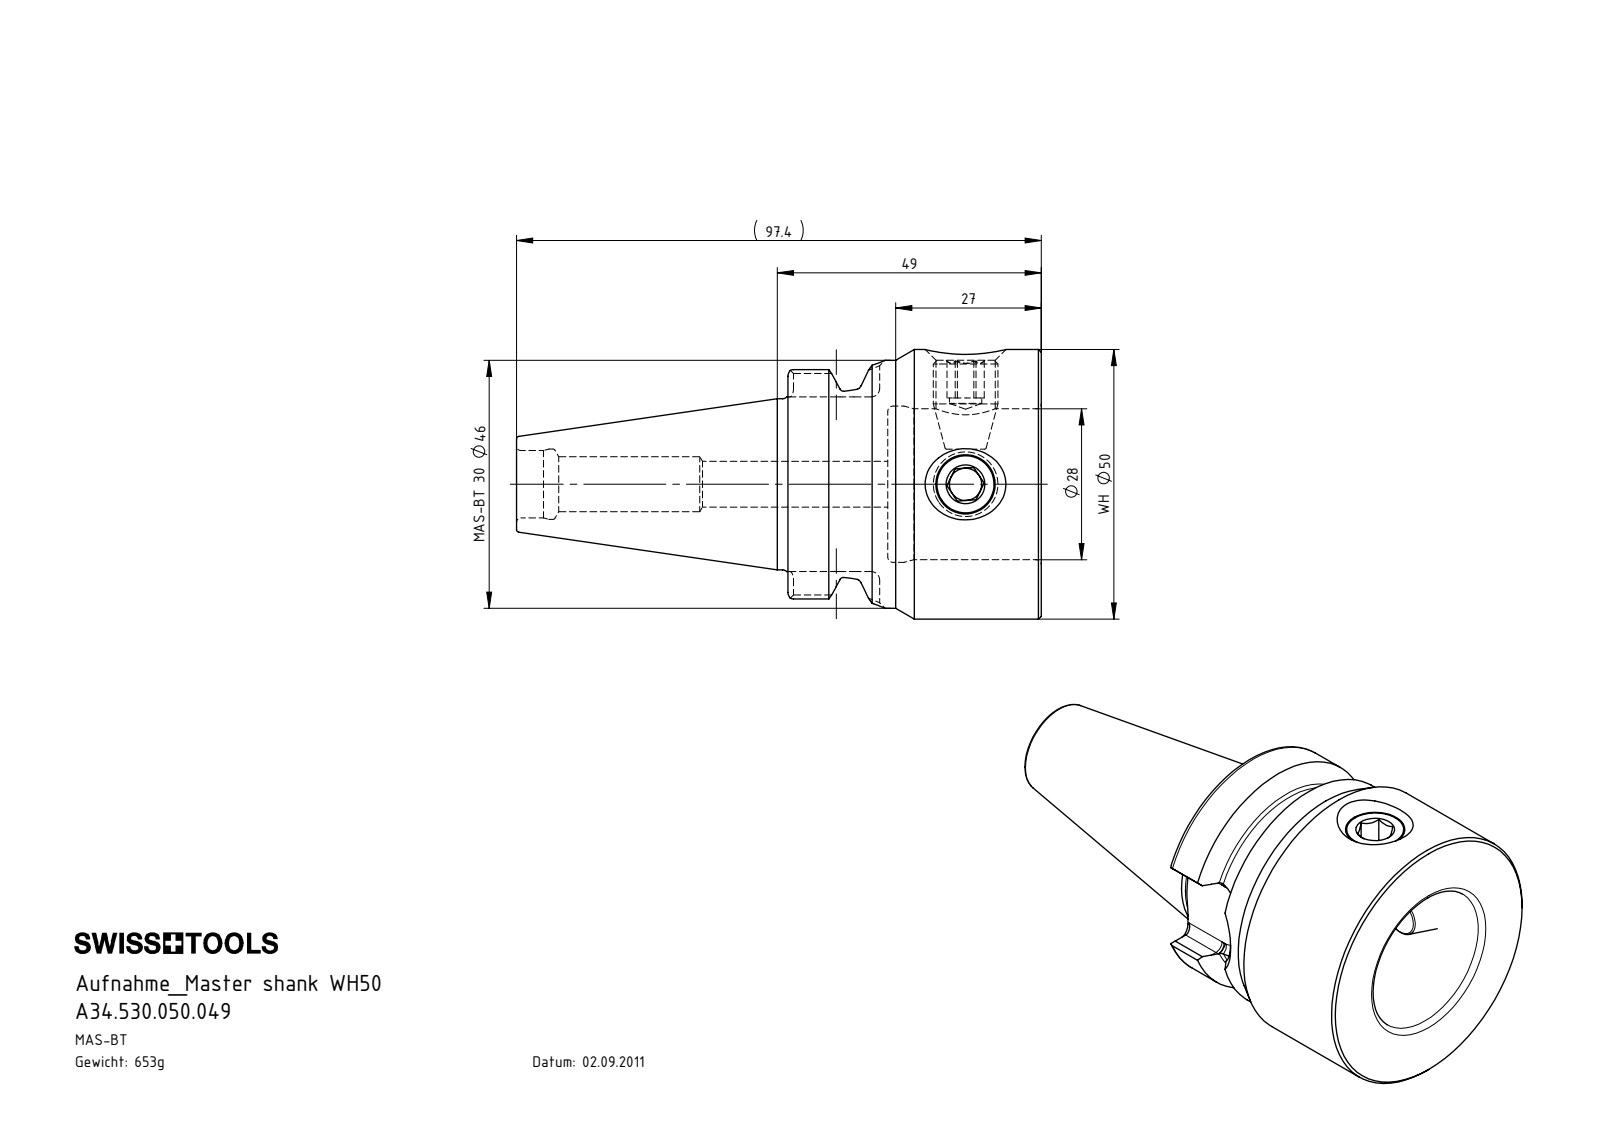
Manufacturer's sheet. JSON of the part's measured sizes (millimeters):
{"part_name": "BT3-WH5.K01.049_B; BT3.WH5.K01.049; WH5-ER1.001.017", "step_written_by": "SolidWorks 2017 (AUTOMOTIVE_DESIGN)", "units": "millimeters", "bodies": {"solids": 3, "faces": 141, "planar": 47, "cylindrical": 33, "other": 61}, "overall_size": [97.4, 50, 50], "volume_mm3": 83140, "surface_area_mm2": 20999, "round_holes": [[6, 2], [11, 2], [8.5, 1], [10.2, 1], [12.5, 1], [13.05, 1], [28, 1], [29, 1]], "round_bosses_or_shafts": [[12, 2], [50, 1], [46, 1], [31.75, 1]], "partial_cylinders_radius": [[1.6, 8], [8.05, 1], [19, 1]], "face_to_face_distances": [28.5, 18.5, 47, 32.4, 6, 16.5, 50.4, 68.9, 97.4, 6.8]}
